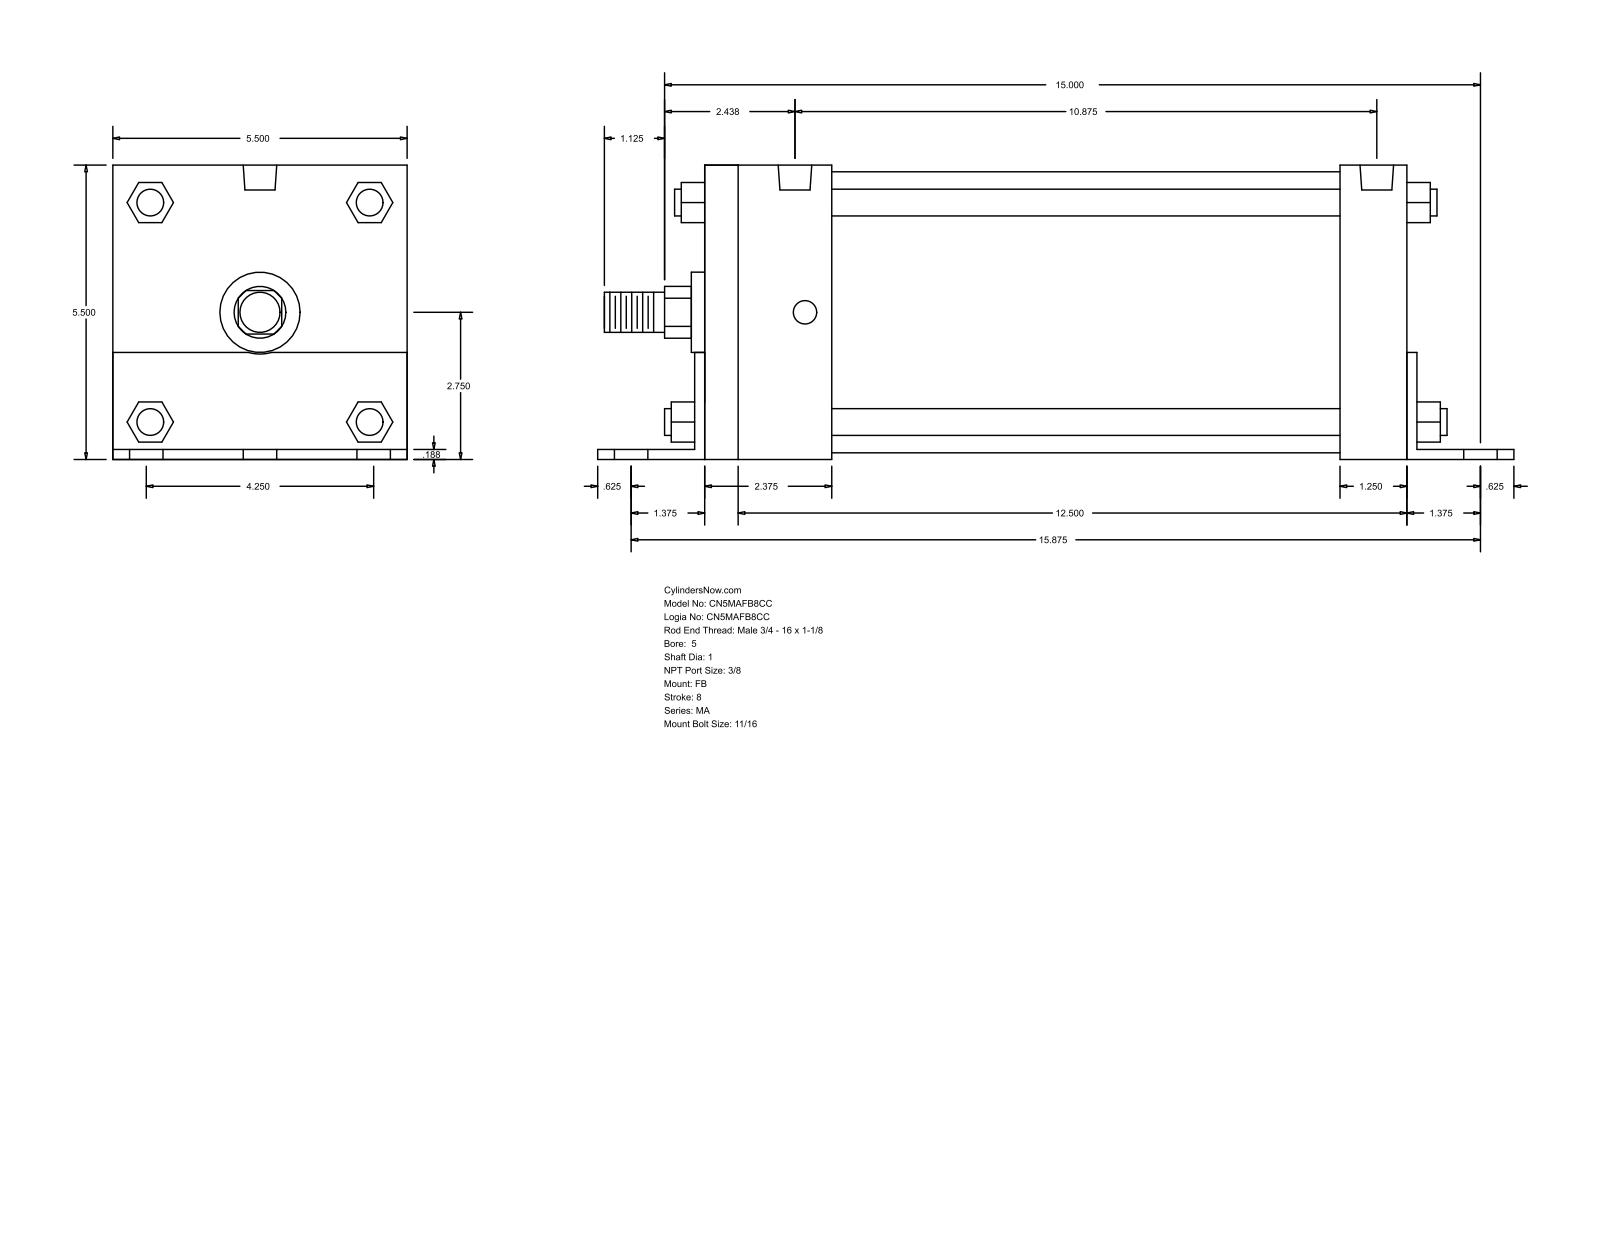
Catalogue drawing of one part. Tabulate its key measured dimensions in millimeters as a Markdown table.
| quantity | value |
| --- | --- |
| part name | MA_FB__0500_1 |
| STEP written by | GSSL Pune (CONFIG_CONTROL_DESIGN) |
| units | millimeters |
| bodies | 0 solids, 140 faces (105 planar, 35 cylindrical, 0 other) |
| overall size | 434.98 × 139.75 × 139.7 |
| round holes (diameter × count) | 17.46 × 6, 11.11 × 4, 15.93 × 2 |
| round bosses / shafts (diameter × count) | 12.7 × 4, 133.35 × 1, 38.1 × 1, 25.4 × 1, 19.05 × 1 |
| partial cylindrical surfaces (radius × count) | 12.29 × 1, 19.81 × 1 |
| main face-to-face distances | 139.7, 4.76, 139.75, 338.14, 4.71, 134.99, 333.38, 342.9, 31.75, 36.51 |
| hole center spacings | 53.98, 406.83, 403.23, 4.76, 73.04, 76.33, 94.68, 98.63 |
